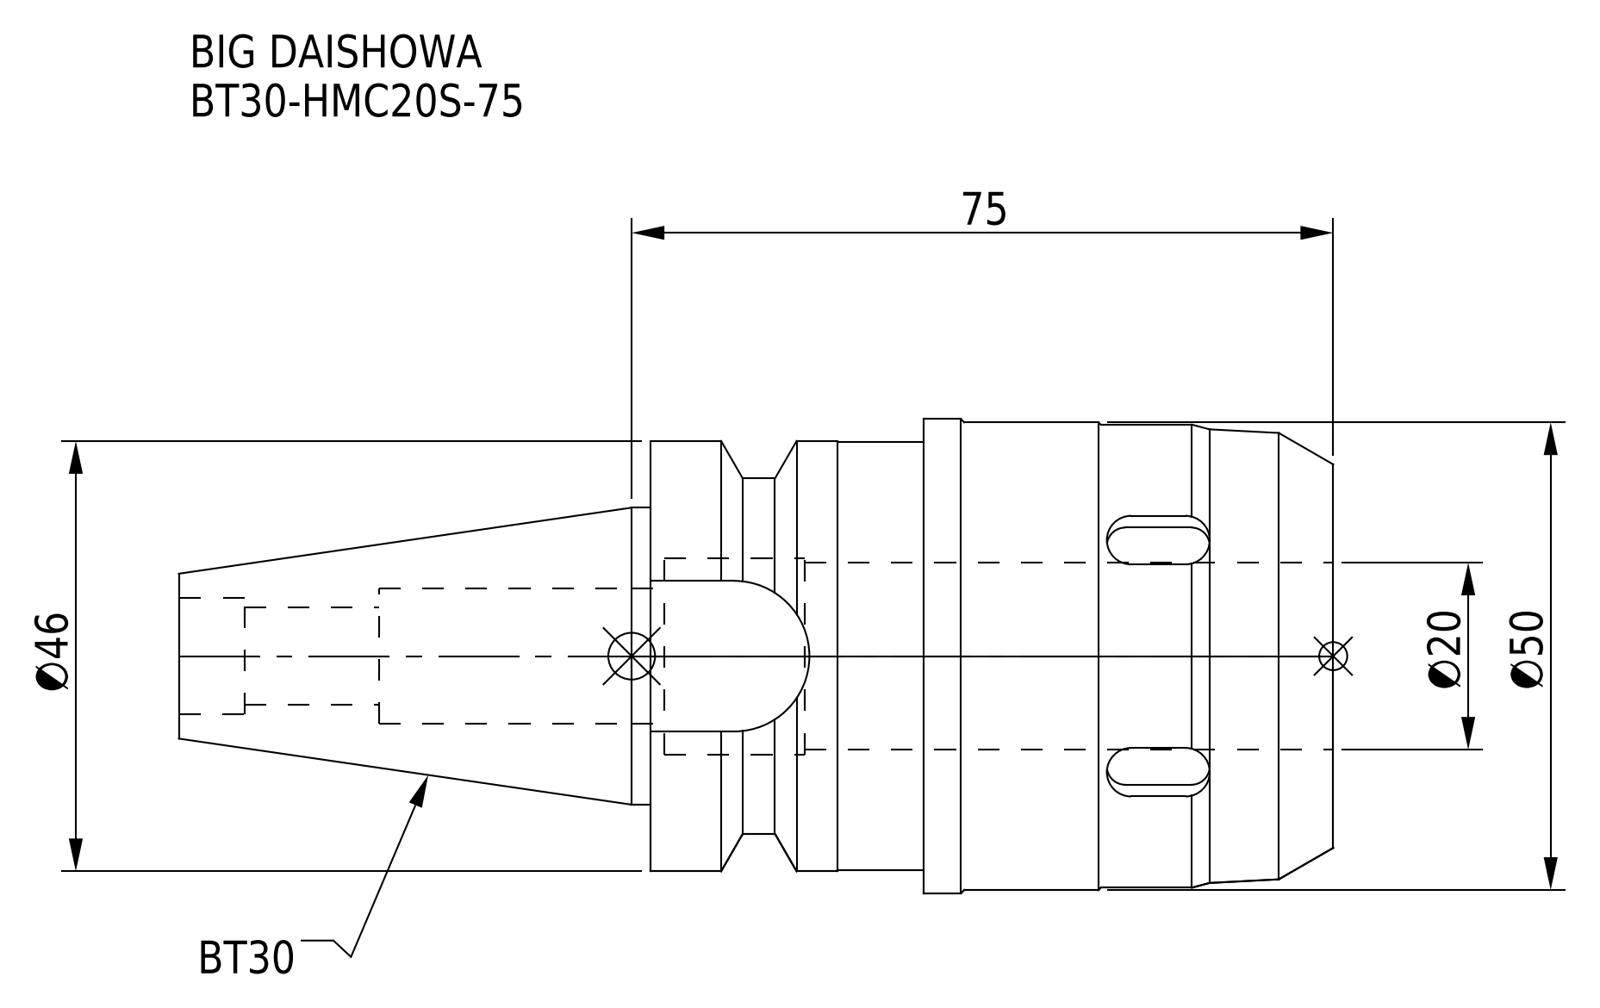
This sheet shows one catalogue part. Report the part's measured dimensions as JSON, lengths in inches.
{"part_name": "BT30-HMC20S-75", "step_written_by": "CREO PARAMETRIC BY PTC INC, 2016380 (AUTOMOTIVE_DESIGN)", "units": "inches", "bodies": {"solids": 1, "faces": 95, "planar": 33, "cylindrical": 42, "other": 20}, "overall_size": [4.858, 1.996, 1.996], "volume_in3": 7.305, "surface_area_in2": 39.29, "round_holes": [[0.409, 1], [0.492, 1], [0.571, 1], [0.787, 1], [0.827, 1]], "round_bosses_or_shafts": [[1.996, 1], [1.969, 1], [1.949, 1], [1.811, 1], [1.803, 1], [1.25, 1]], "partial_cylinders_radius": [[0.118, 6], [0.317, 1], [0.748, 1]], "face_to_face_distances": [2.874, 1.724, 1.15, 1.283, 2.815, 1.091, 0.059, 1.772, 4.858, 3.134]}
